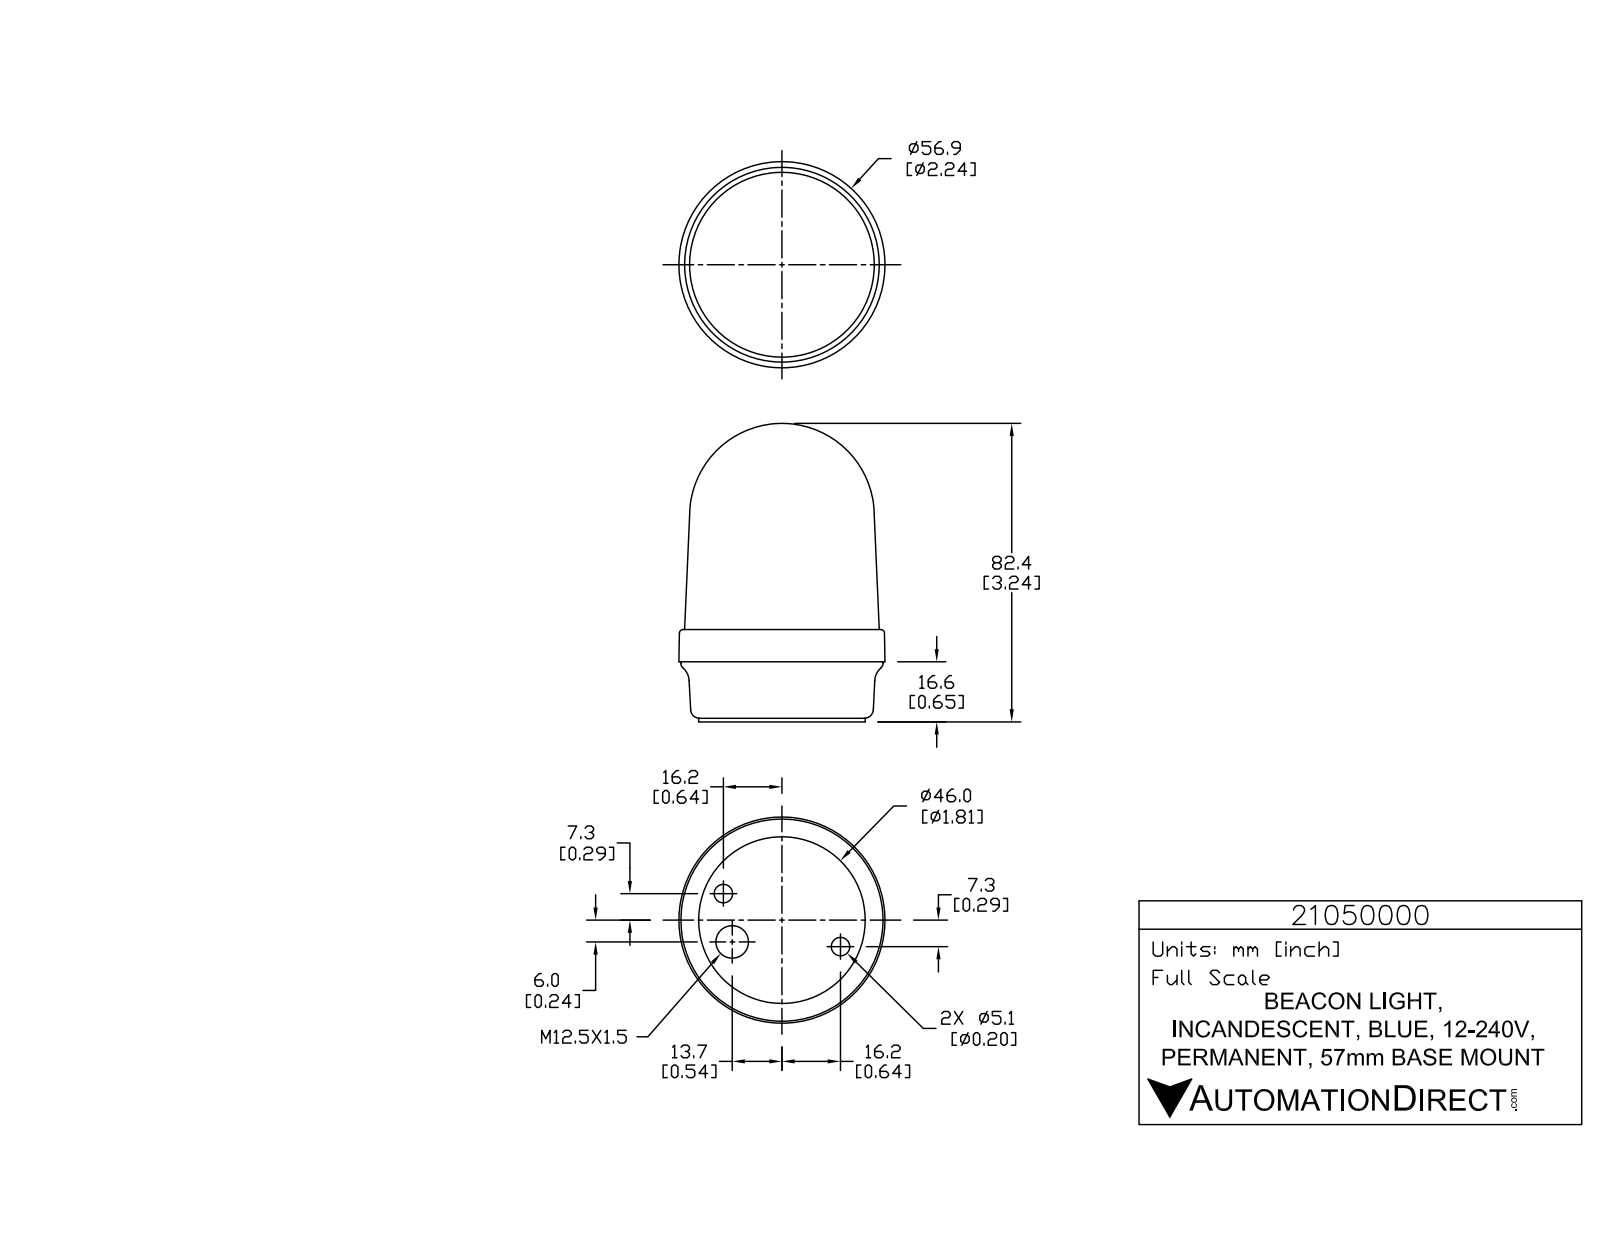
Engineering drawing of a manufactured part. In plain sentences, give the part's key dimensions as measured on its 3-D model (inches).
The part is named "21050000". Its 3-D file was written by "SolidWorks 2015 (AUTOMOTIVE_DESIGN)". It is 1 solid with 778 faces: 526 planar, 160 cylindrical and 92 other. Overall it measures 3.244 by 2.24 by 2.24 inches. Its volume is 9.7 cubic inches and its surface area 24.8 square inches. Round holes: 3 of diameter 0.039, 2 of diameter 0.201, 1 of diameter 0.354. Round bosses or shafts: 3 of diameter 0.226, 3 of diameter 0.056, 1 of diameter 2.197, 1 of diameter 1.811. Partial cylindrical surfaces (rounded edges, fillets, slot ends): 6 of radius 0.008, 6 of radius 0.008, 6 of radius 0.008, 6 of radius 0.131, 3 of radius 0.004, 3 of radius 0.005, 3 of radius 0.008, 3 of radius 0.008. The main face-to-face distances are 0.039, 0.654, 0.614, 1.004, 0.965, 0.35, 0.418, 1.422, 1.382, 0.768. The hole center spacings are 0.534, 1.179, 1.398.
